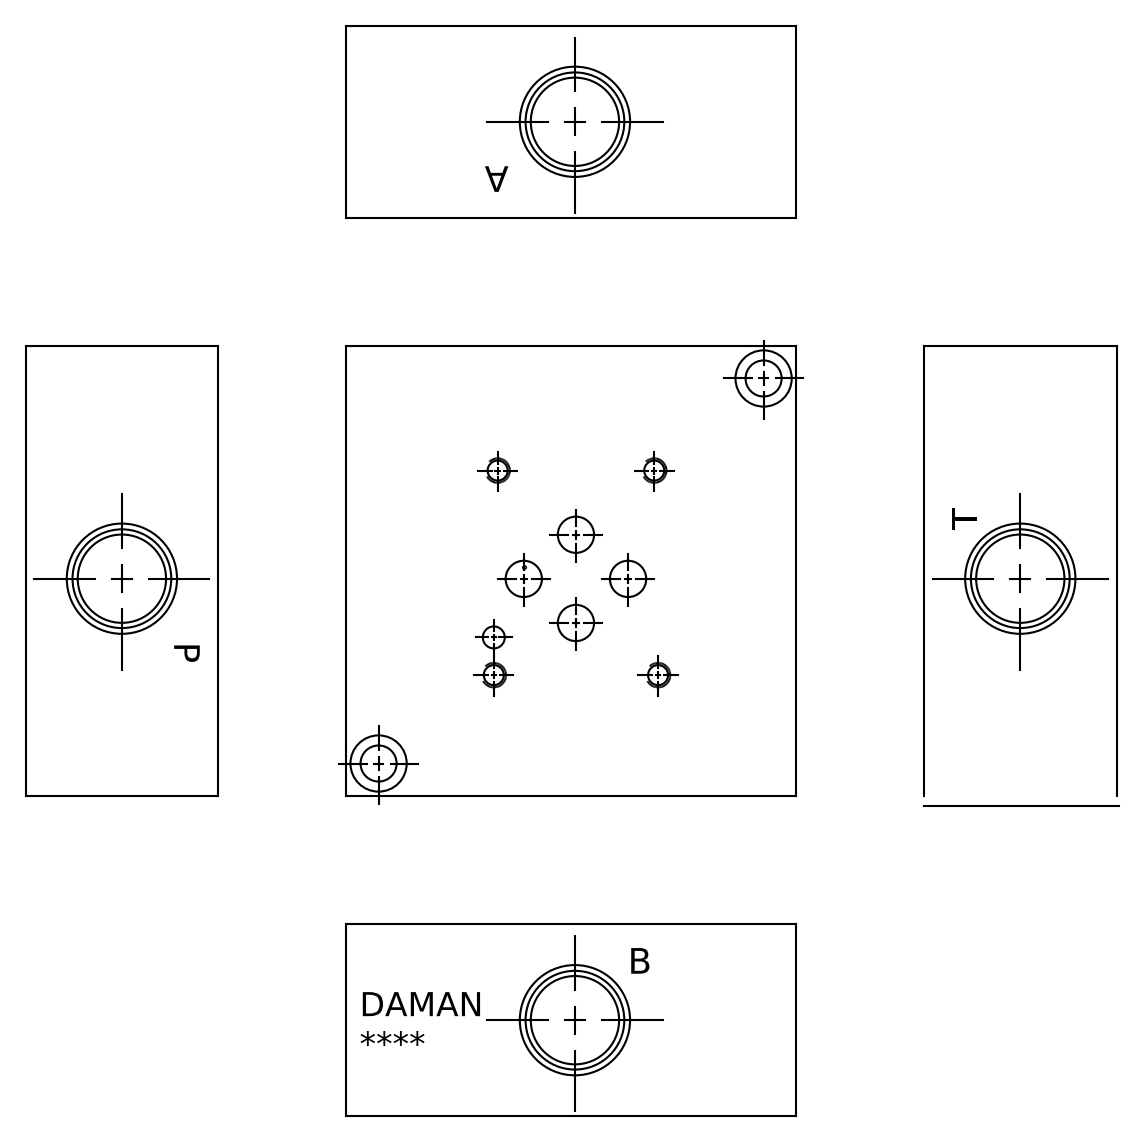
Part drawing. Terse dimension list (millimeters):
name: Part_AD03SPS8P.B02090R1_3D
written by: Autodesk Inventor 2019 (AUTOMOTIVE_DESIGN)
unit: mm
bodies: 1 solid, 443 faces (269 planar, 25 cylindrical, 149 other)
size: 88.9 × 88.9 × 38.1
volume: 270 588 mm³; area: 37 427 mm²
holes: 5× ⌀3.78, 4× ⌀4.83, 4× ⌀7.14, 2× ⌀7.16, 2× ⌀10.31, 2× ⌀17.48, 2× ⌀21.59
face distances: 38.1, 88.9, 15.37, 73.53, 58.16, 1, 87.9, 14.37, 72.53, 28.57
hole spacings: 13.52, 13.54, 19.95, 22.05, 32.72, 33.55, 40.5, 51.45
